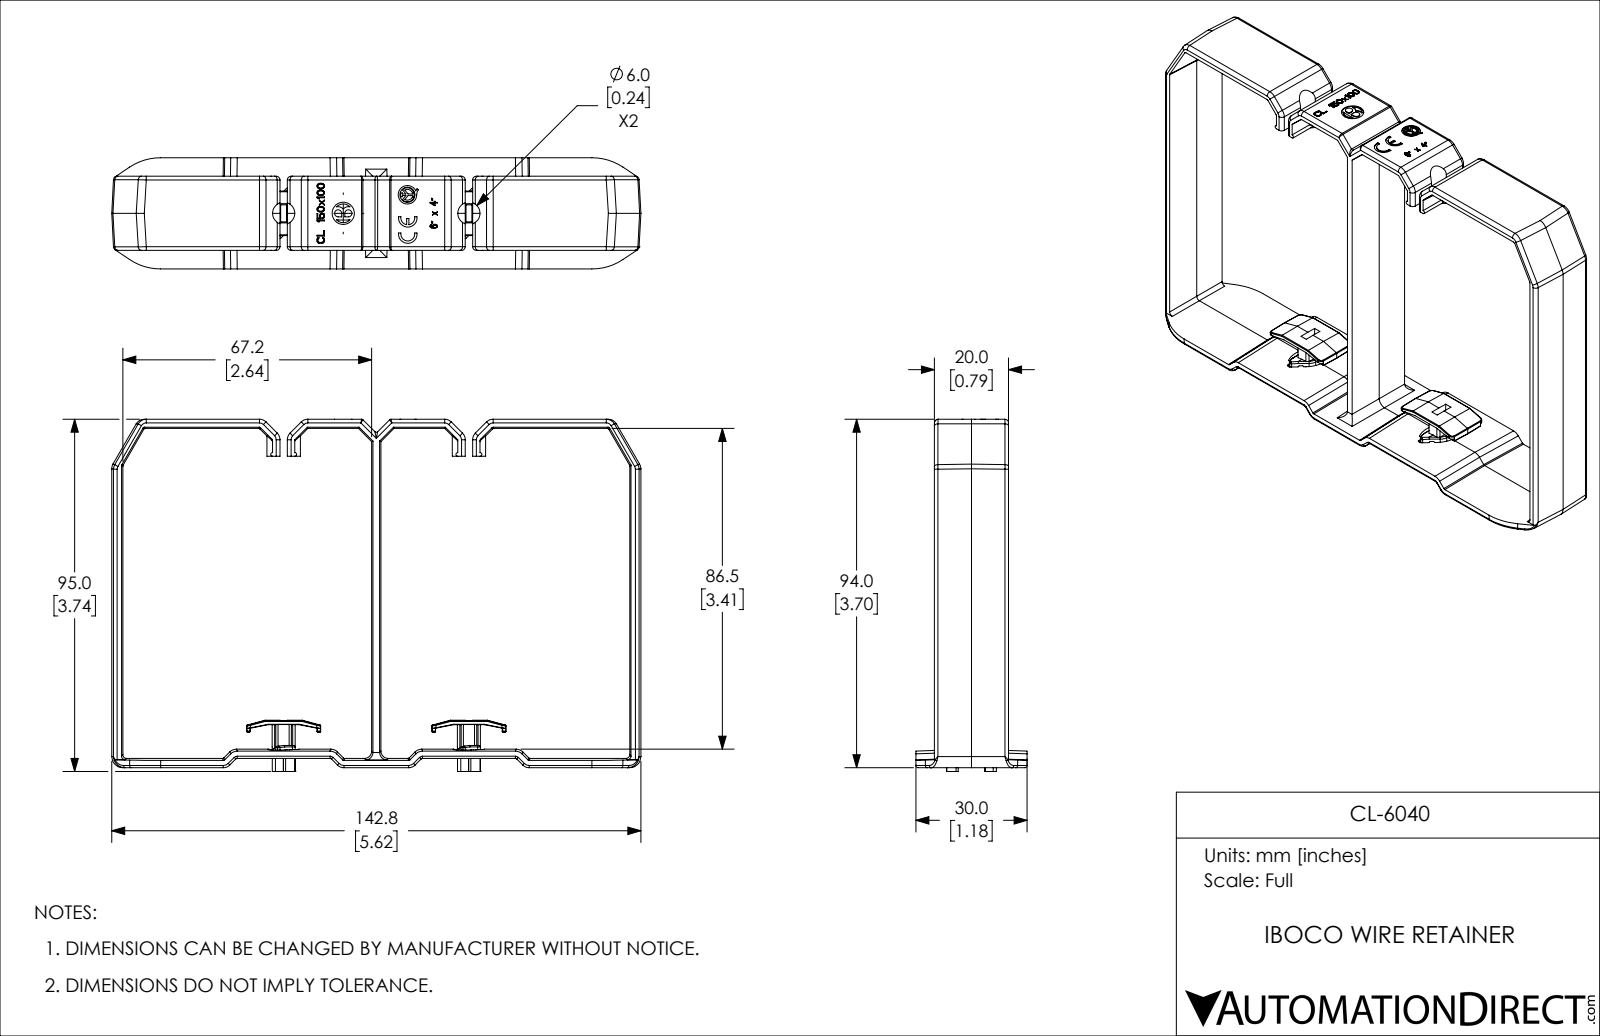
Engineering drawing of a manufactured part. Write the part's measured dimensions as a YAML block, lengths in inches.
part_name: "CL-6040"
step_written_by: "SolidWorks 2019 (CONFIG_CONTROL_DESIGN)"
units: inches
bodies: {solids: 1, faces: 1090, planar: 686, cylindrical: 322, other: 82}
overall_size: [5.622, 3.74, 1.181]
volume: 1.807
surface_area: 45.08
round_holes:
  - {diameter: 0.197, count: 1}
  - {diameter: 0.236, count: 1}
round_bosses_or_shafts:
  - {diameter: 0.161, count: 1}
partial_cylinders:
  - {radius: 0.02, count: 47}
  - {radius: 0.039, count: 46}
  - {radius: 0.008, count: 36}
  - {radius: 0.098, count: 34}
  - {radius: 0.024, count: 16}
  - {radius: 0.012, count: 12}
  - {radius: 0.016, count: 12}
  - {radius: 0.079, count: 6}
face_to_face_distances: [0.098, 2.641, 2.739, 3.5, 3.701, 5.38, 5.617, 3.402, 3.602, 1.392]
hole_center_spacings: [0.71]
